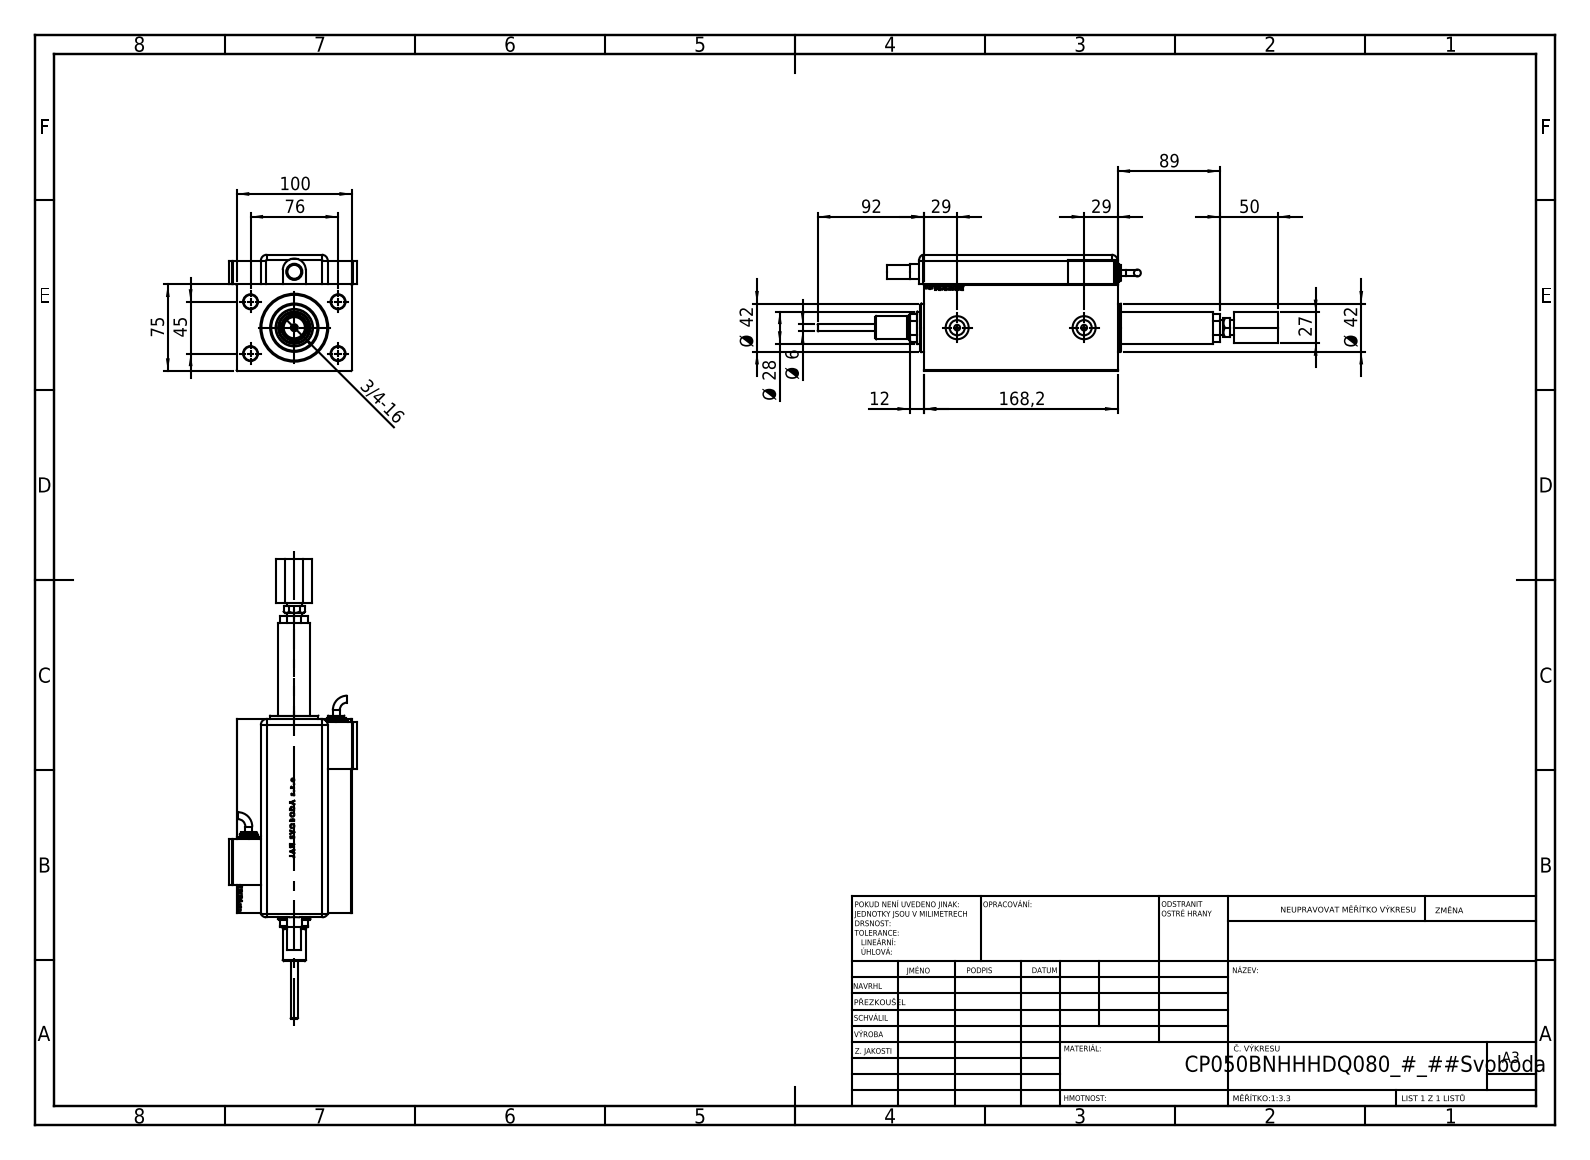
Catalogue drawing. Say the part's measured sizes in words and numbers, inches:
The part is named "V450CP_MALE_METRIC; V450DCP_B_Body; TYC; KRYT (+6 more)". Its 3-D file was written by "SolidWorks 2019 (CONFIG_CONTROL_DESIGN)". It is 11 solids with 1322 faces: 618 planar, 141 cylindrical and 563 other. Overall it measures 15.717 by 4.37 by 3.969 inches. Its volume is 84.15 cubic inches and its surface area 366.5 square inches. Round holes: 4 of diameter 0.157, 4 of diameter 0.472, 2 of diameter 0.197, 2 of diameter 0.315, 2 of diameter 0.383, 2 of diameter 0.518, 2 of diameter 0.591, 2 of diameter 0.787, 1 of diameter 0.118, 1 of diameter 0.236, 1 of diameter 0.551, 1 of diameter 0.728. Round bosses or shafts: 3 of diameter 0.787, 2 of diameter 0.63, 2 of diameter 0.551, 2 of diameter 0.236, 1 of diameter 1.654, 1 of diameter 0.709, 1 of diameter 0.512, 1 of diameter 0.503. Partial cylindrical surfaces (rounded edges, fillets, slot ends): 9 of radius 0.197, 1 of radius 0.394, 1 of radius 0.531. The main face-to-face distances are 2.953, 0.118, 3.937, 3.969, 1.016, 6.622, 0.945, 0.039, 3.85, 0.898. The hole center spacings are 1.739, 1.772, 1.813, 2.992, 3.17, 3.477, 0.787, 0.804.
